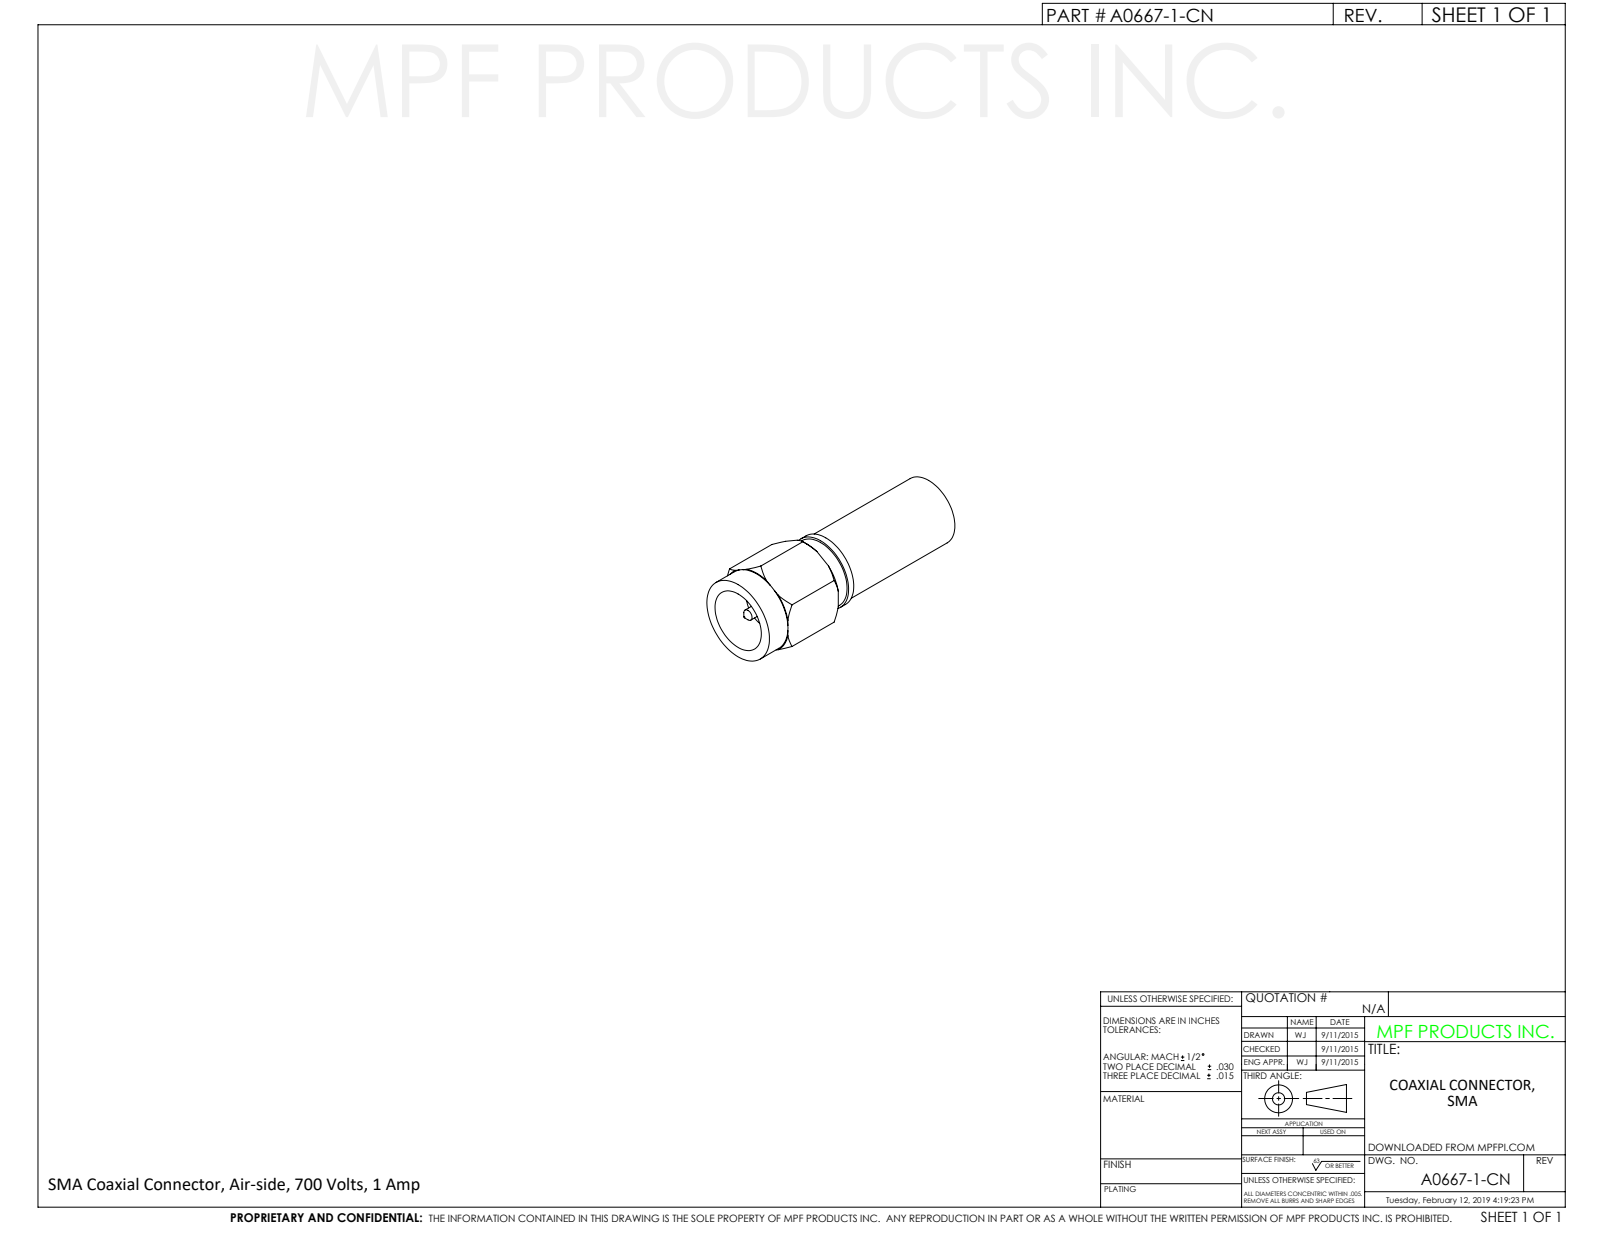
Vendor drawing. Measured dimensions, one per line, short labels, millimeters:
name: A0667-1-CN
written by: SolidWorks 2012 (CONFIG_CONTROL_DESIGN)
unit: mm
bodies: 2 solids, 54 faces (22 planar, 30 cylindrical, 2 other)
size: 22.4 × 8.9 × 8.9
volume: 430 mm³; area: 1 442 mm²
holes: 1× ⌀2.9, 1× ⌀4.2, 1× ⌀6.6, 1× ⌀7.3, 1× ⌀7.4, 1× ⌀8.2
bosses: 1× ⌀8.9, 1× ⌀8.7, 1× ⌀7.6, 1× ⌀7.1, 1× ⌀6.4, 1× ⌀4.9, 1× ⌀4.6
face distances: 7.7, 12, 10.7, 1.3, 5.7, 5, 6.2, 0.6, 3.7, 1.1
